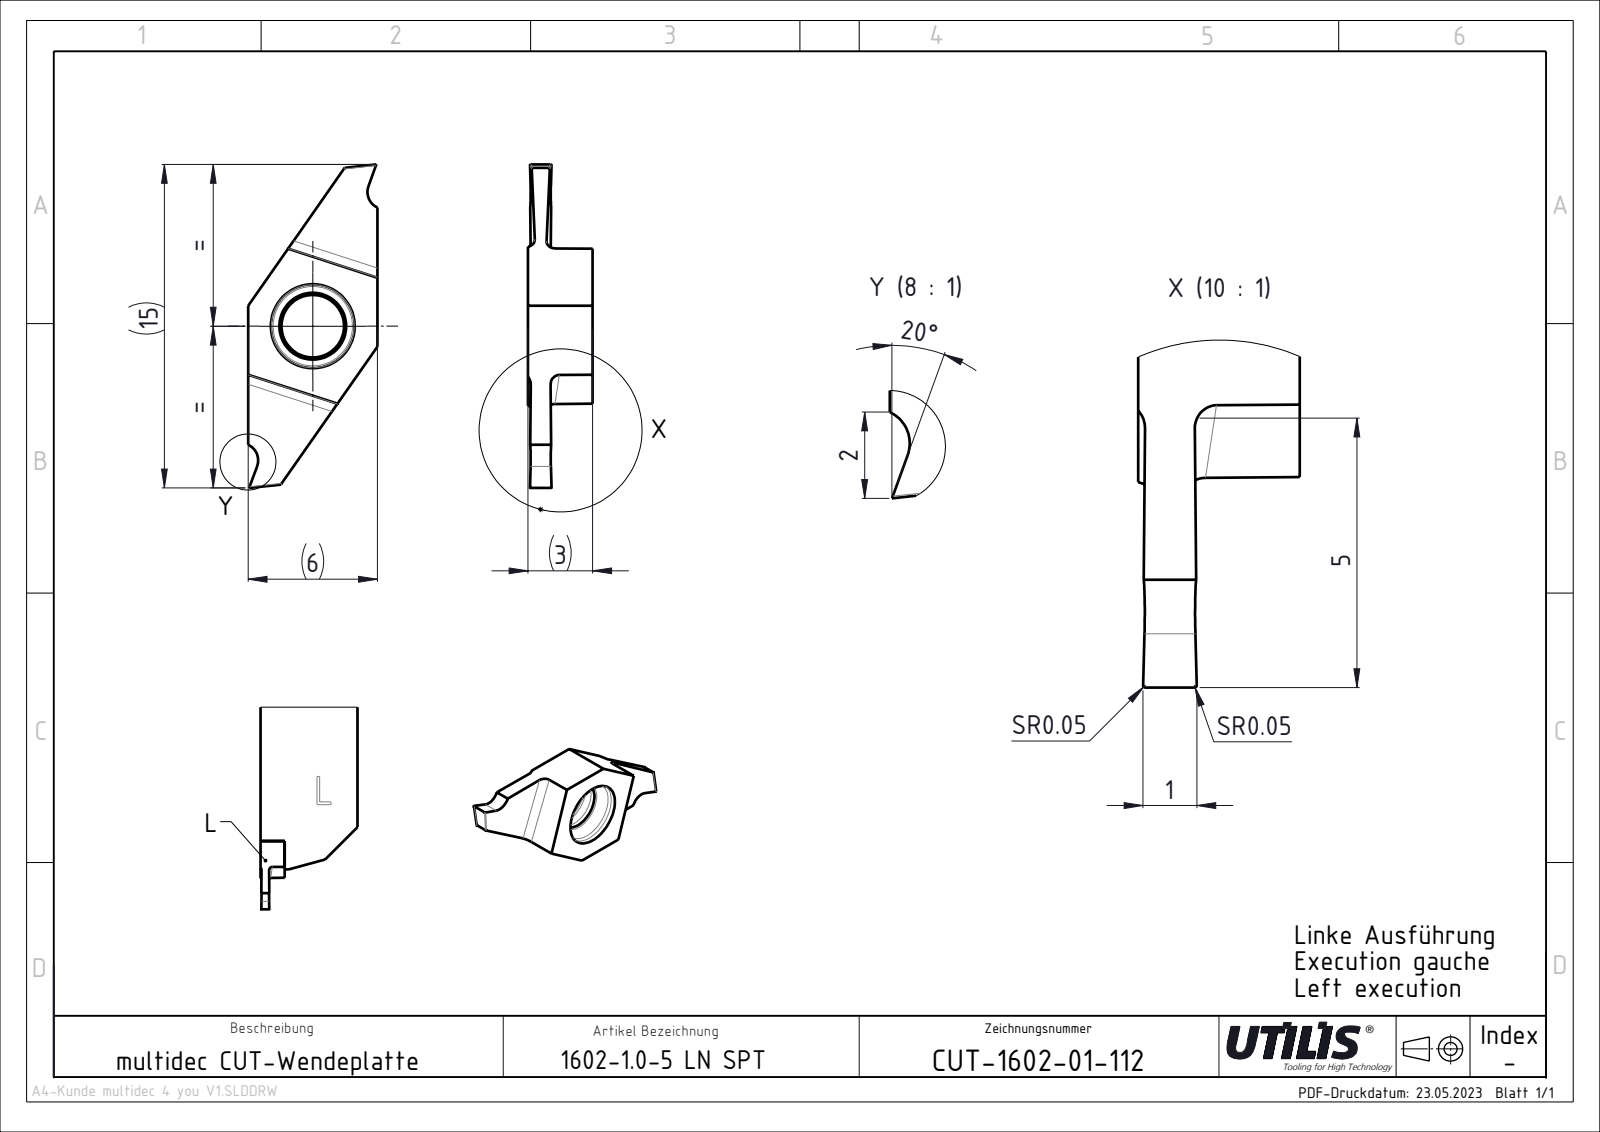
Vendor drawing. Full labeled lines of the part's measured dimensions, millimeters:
Part name (STEP PRODUCT): 1602-CUT-1602-01-112 stp
STEP written by: SolidWorks 2022 (AUTOMOTIVE_DESIGN)
Units: millimetres
Bodies: 1 solid, 23 faces (14 planar, 9 cylindrical, 0 other)
Overall size (bounding box): 15 × 6 × 3
Volume: 105 mm³ · Surface area: 210 mm²
Round holes (diameter × count): ⌀2.9 ×1
Partial cylindrical surfaces — rounded edges, fillets, slot ends (radius × count): R0.4 ×4
Main face-to-face distances: 6, 3, 0.84, 15
